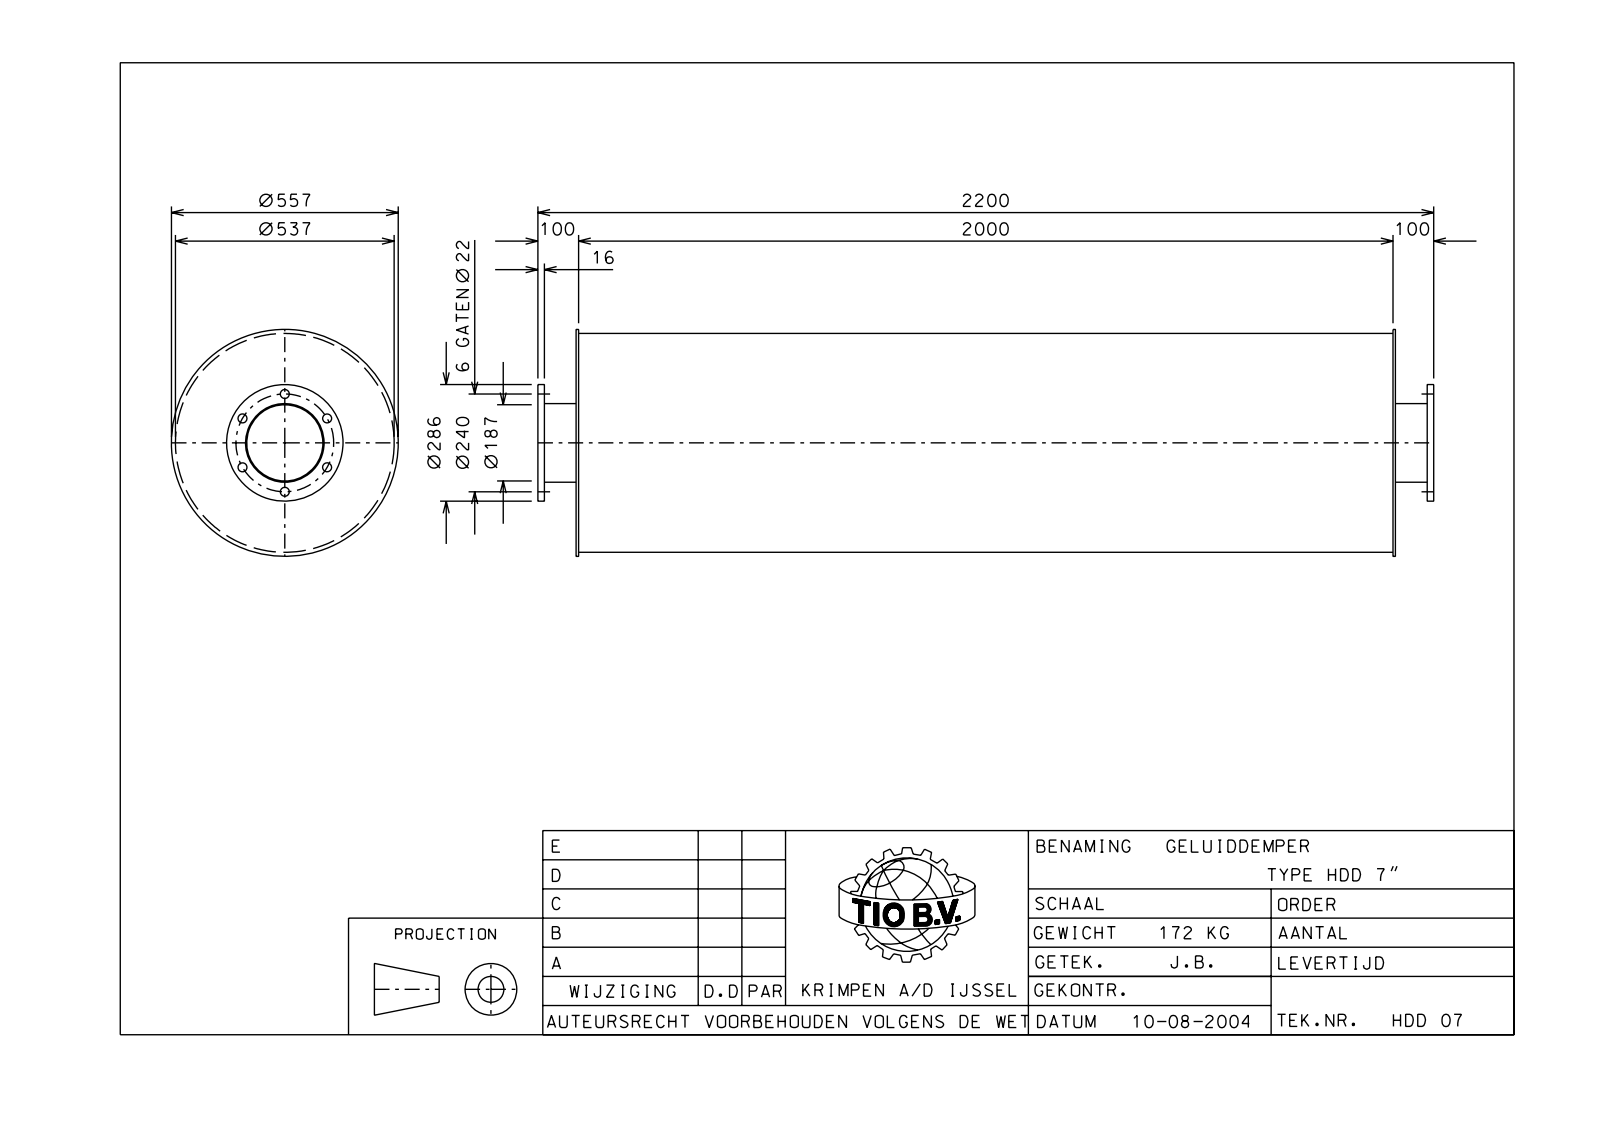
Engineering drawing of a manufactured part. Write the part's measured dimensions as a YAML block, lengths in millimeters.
part_name: "MAAT3D"
step_written_by: "Autodesk Inventor 2015 (AUTOMOTIVE_DESIGN)"
units: millimeters
bodies: {solids: 7, faces: 40, planar: 14, cylindrical: 26, other: 0}
overall_size: [2200, 557, 557]
volume: 13570000
surface_area: 8023000
round_holes:
  - {diameter: 22, count: 6}
  - {diameter: 187, count: 1}
  - {diameter: 195, count: 1}
  - {diameter: 531, count: 1}
round_bosses_or_shafts:
  - {diameter: 557, count: 1}
  - {diameter: 537, count: 1}
  - {diameter: 286, count: 1}
  - {diameter: 193, count: 1}
face_to_face_distances: [5, 2005, 2000, 2010, 95, 2100, 100, 2105, 2184, 79]
hole_center_spacings: [120, 207.84, 239.99, 240]
